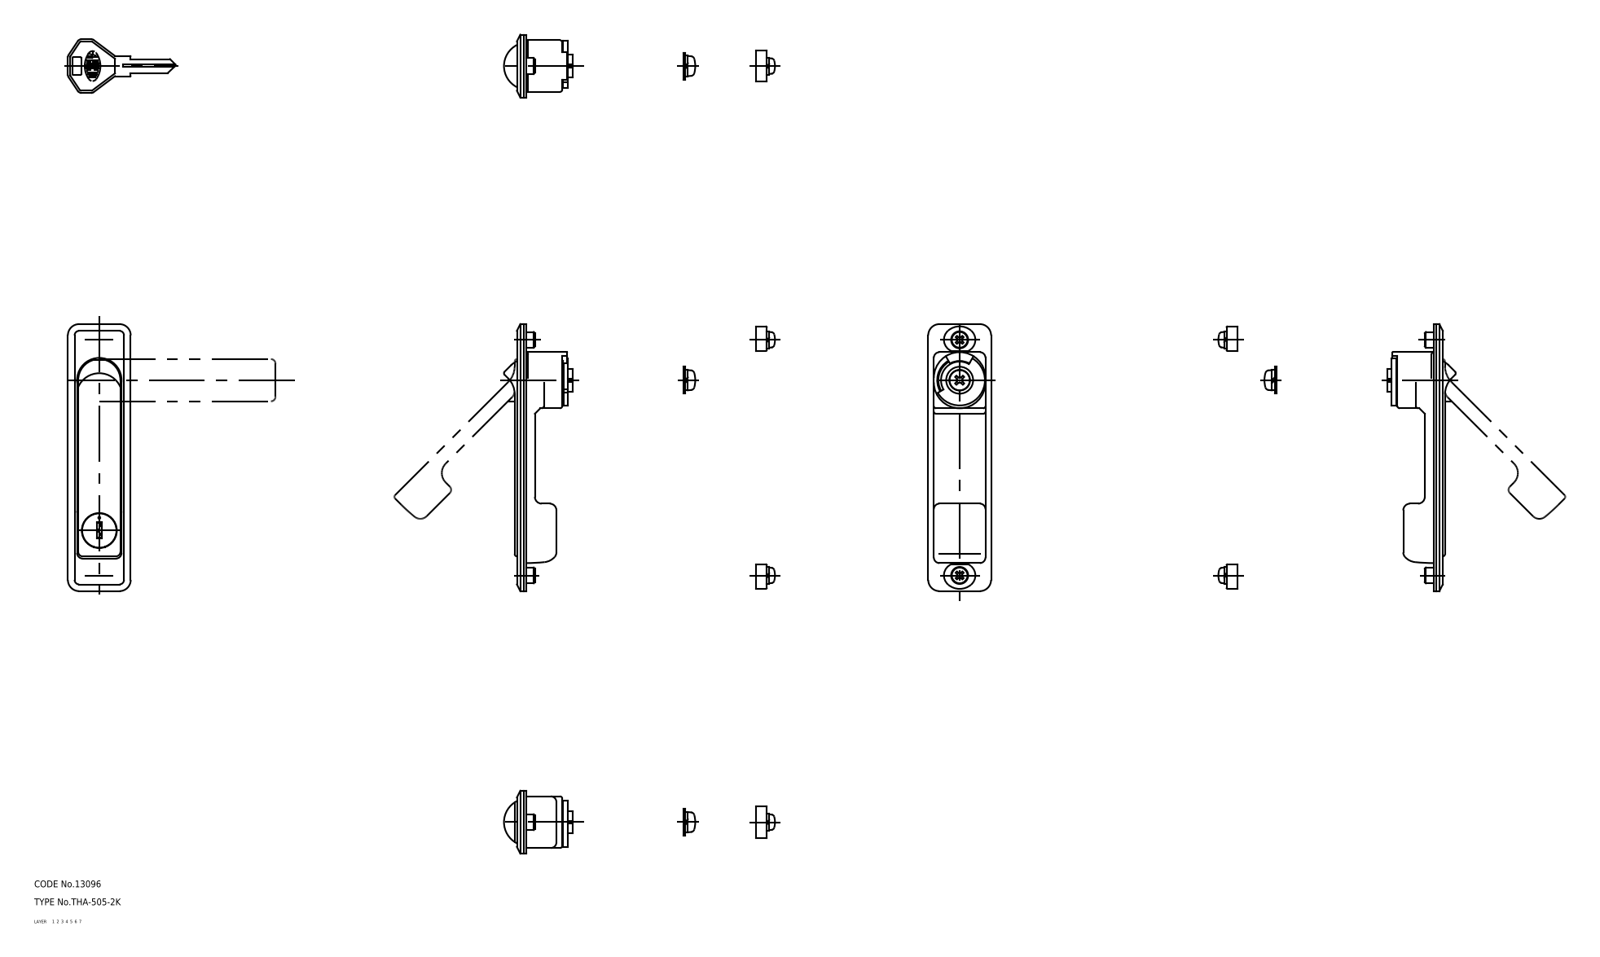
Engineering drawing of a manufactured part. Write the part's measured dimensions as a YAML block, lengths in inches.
part_name: "lock; key; screw_B; bracket (+8 more)"
step_written_by: "CADfix (AUTOMOTIVE_DESIGN)"
units: inches
bodies: {solids: 13, faces: 439, planar: 0, cylindrical: 0, other: 439}
overall_size: [4.685, 3.698, 1.102]
volume: 1.976
surface_area: 43.61
